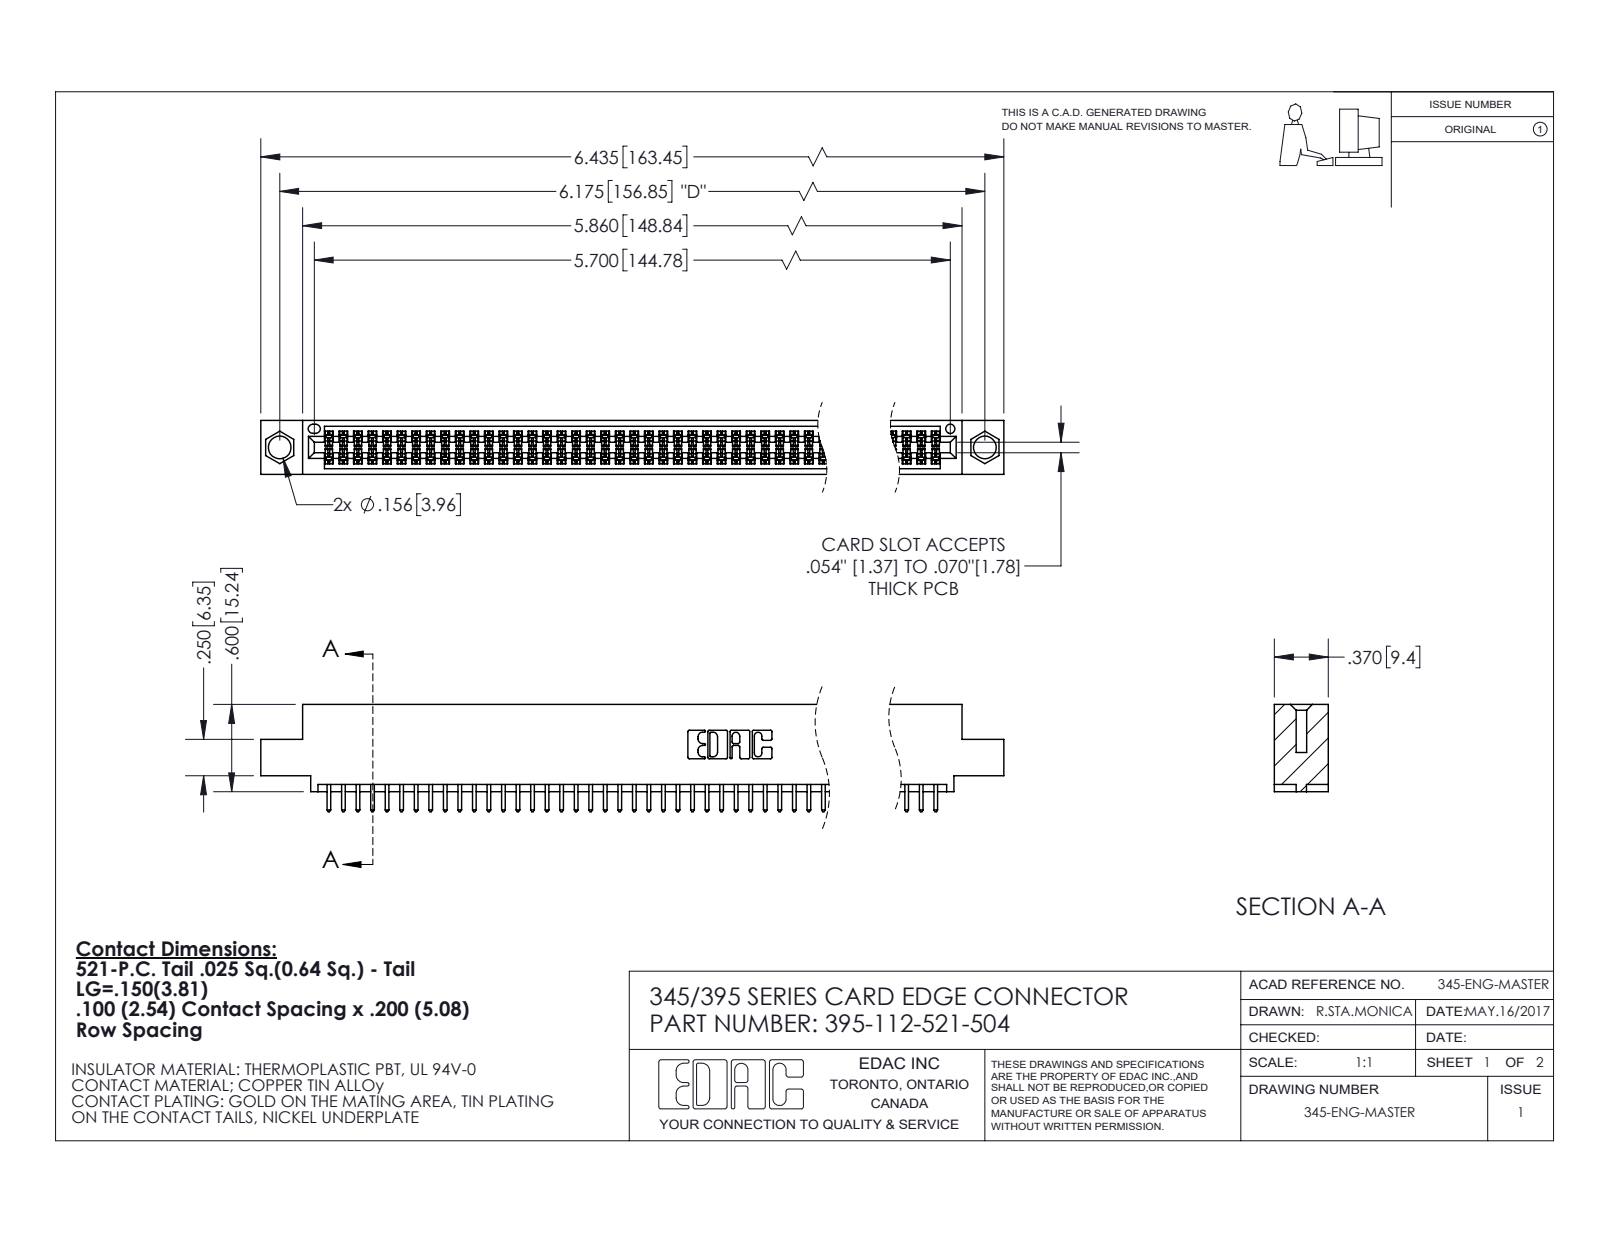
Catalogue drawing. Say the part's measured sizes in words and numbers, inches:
The part is named "345-292-001_345-293-121; 345 Part_0.110 Offset - 0.156 Dia-TI; 395-112-521-504". Its 3-D file was written by "SolidWorks 2020 (CONFIG_CONTROL_DESIGN)". It is 113 solids with 5744 faces: 3794 planar, 1950 cylindrical and 0 other. Overall it measures 6.435 by 0.737 by 0.37 inches. Its volume is 0.963 cubic inches and its surface area 36.03 square inches. Round holes: 2 of diameter 0.156, 1 of diameter 0.064. Partial cylindrical surfaces (rounded edges, fillets, slot ends): 224 of radius 0.006, 112 of radius 0.01, 22 of radius 0.01, 6 of radius 0.007, 6 of radius 0.031, 3 of radius 0.026, 2 of radius 0.014, 2 of radius 0.019. The main face-to-face distances are 0.298, 0.072, 0.2, 0.098, 0.272, 0.025, 0.37, 0.225, 0.175, 0.149. The hole center spacings are 0.27, 5.939, 6.175.
